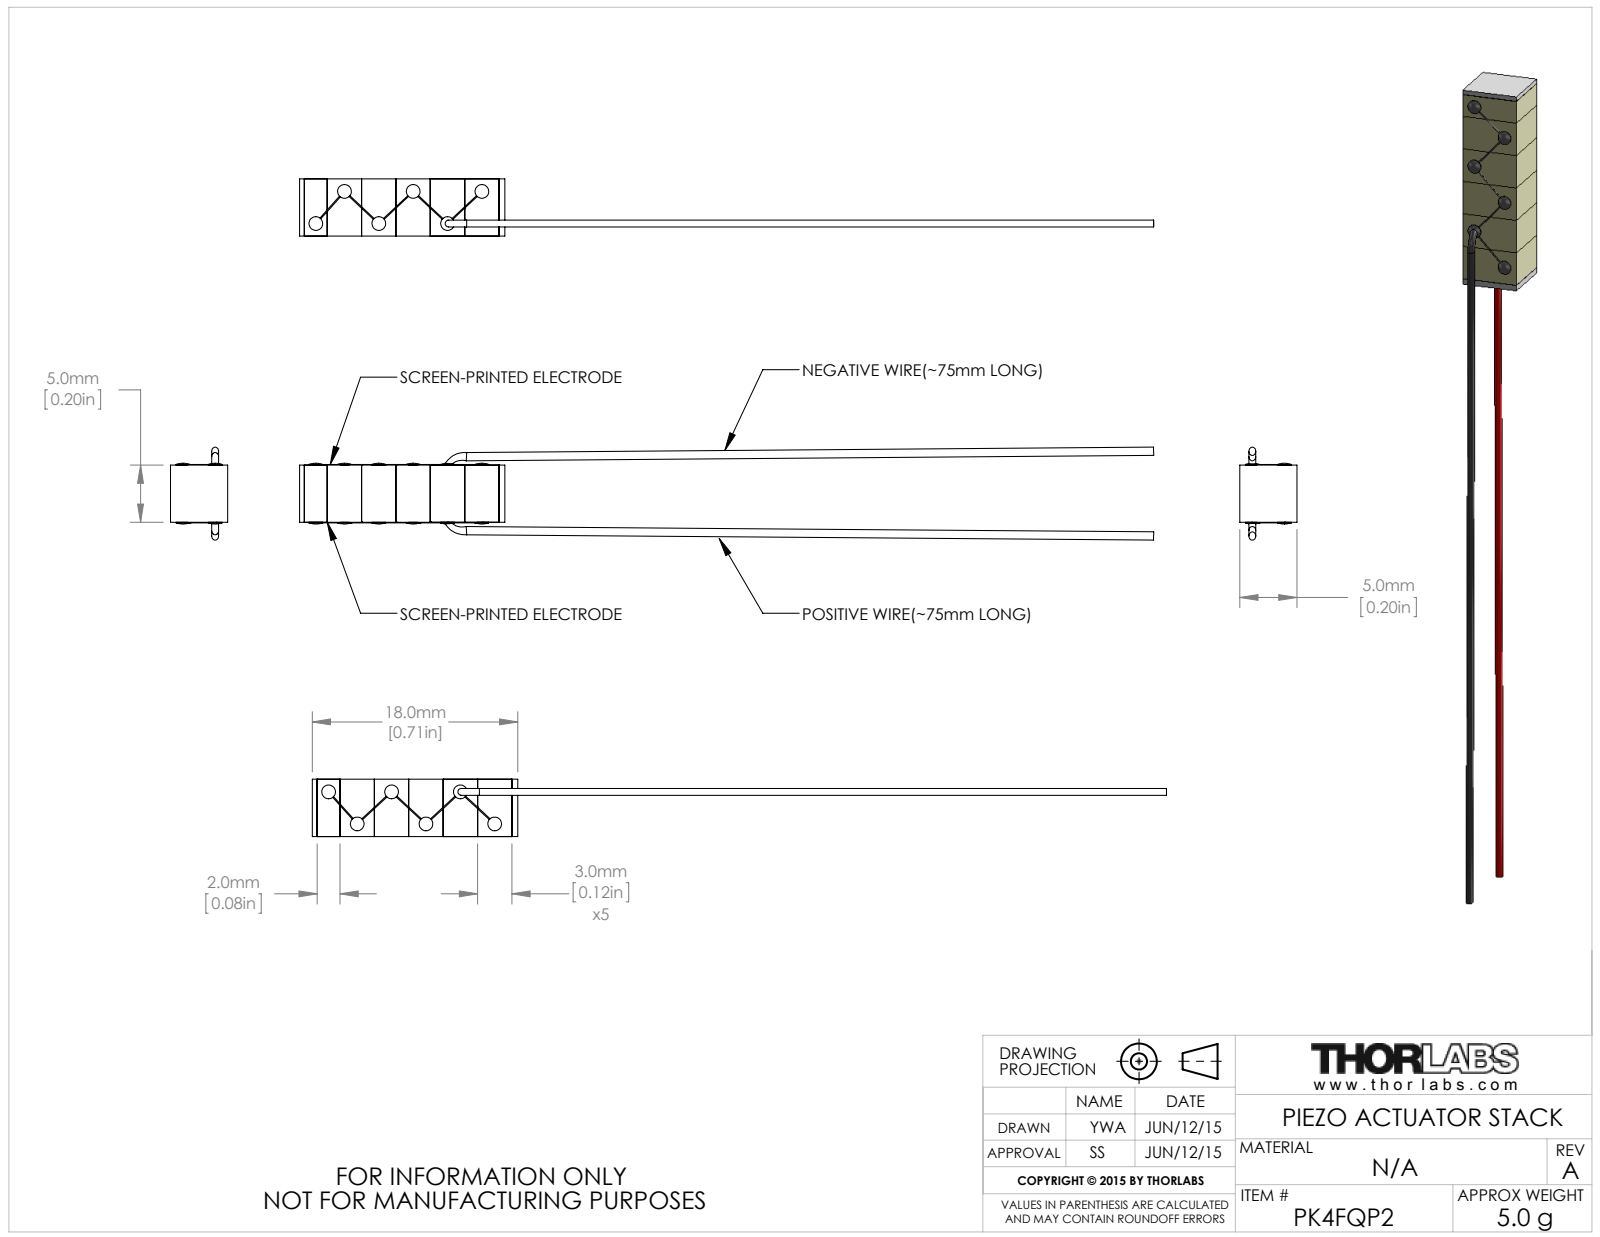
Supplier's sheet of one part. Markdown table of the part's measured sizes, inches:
| quantity | value |
| --- | --- |
| part name | CTN002965 |
| STEP written by | SolidWorks 2014 (AUTOMOTIVE_DESIGN) |
| units | inches |
| bodies | 15 solids, 164 faces (88 planar, 44 cylindrical, 32 other) |
| overall size | 2.936 × 0.32 × 0.197 |
| volume | 0.042 in³ |
| surface area | 2.111 in² |
| round bosses / shafts (diameter × count) | 0.047 × 6 |
| main face-to-face distances | 0.197, 0.118, 0.236, 0.354, 0.472, 0.551, 0.433, 0.079, 0.591, 0.669 |
